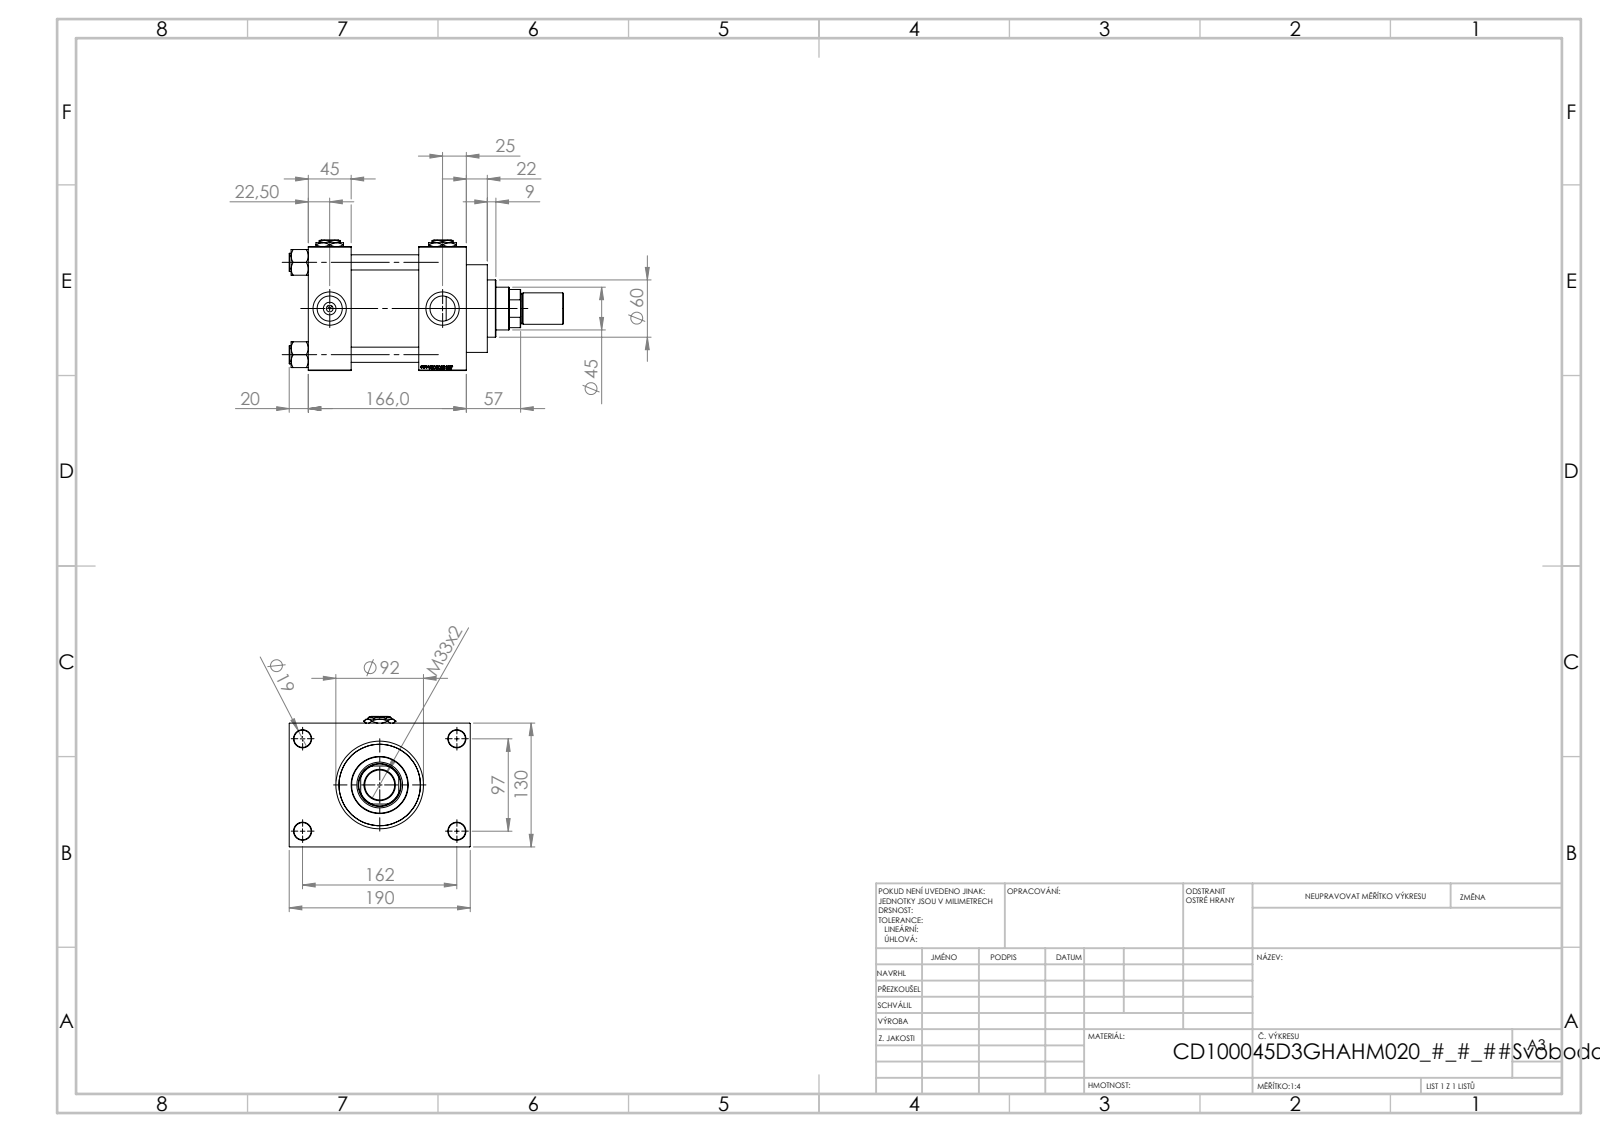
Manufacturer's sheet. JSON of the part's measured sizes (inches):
{"part_name": "V215CD_D_Body; V215CD_VCP_D; Zatka_pro_OIL_PORT; V215CD_NUT_M5_D (+3 more)", "step_written_by": "SolidWorks 2019 (CONFIG_CONTROL_DESIGN)", "units": "inches", "bodies": {"solids": 14, "faces": 1266, "planar": 597, "cylindrical": 103, "other": 566}, "overall_size": [11.339, 7.48, 5.394], "volume_in3": 159.5, "surface_area_in2": 570.8, "round_holes": [[0.63, 4], [0.709, 4], [1.041, 4], [1.378, 4], [0.276, 3], [1.24, 1], [1.772, 1], [1.89, 1], [2.992, 1], [3.366, 1], [3.937, 1]], "round_bosses_or_shafts": [[0.748, 4], [4.173, 1], [3.622, 1], [2.362, 1], [1.299, 1], [1.22, 1]], "partial_cylinders_radius": [[0.866, 1]], "face_to_face_distances": [1.772, 5.118, 4.567, 2.795, 6.535, 4.764, 1.969, 1.181, 6.299, 0.787], "hole_center_spacings": [1.281, 2.698, 3.717, 3.815, 4.026, 5.096, 6.367, 3.819]}
